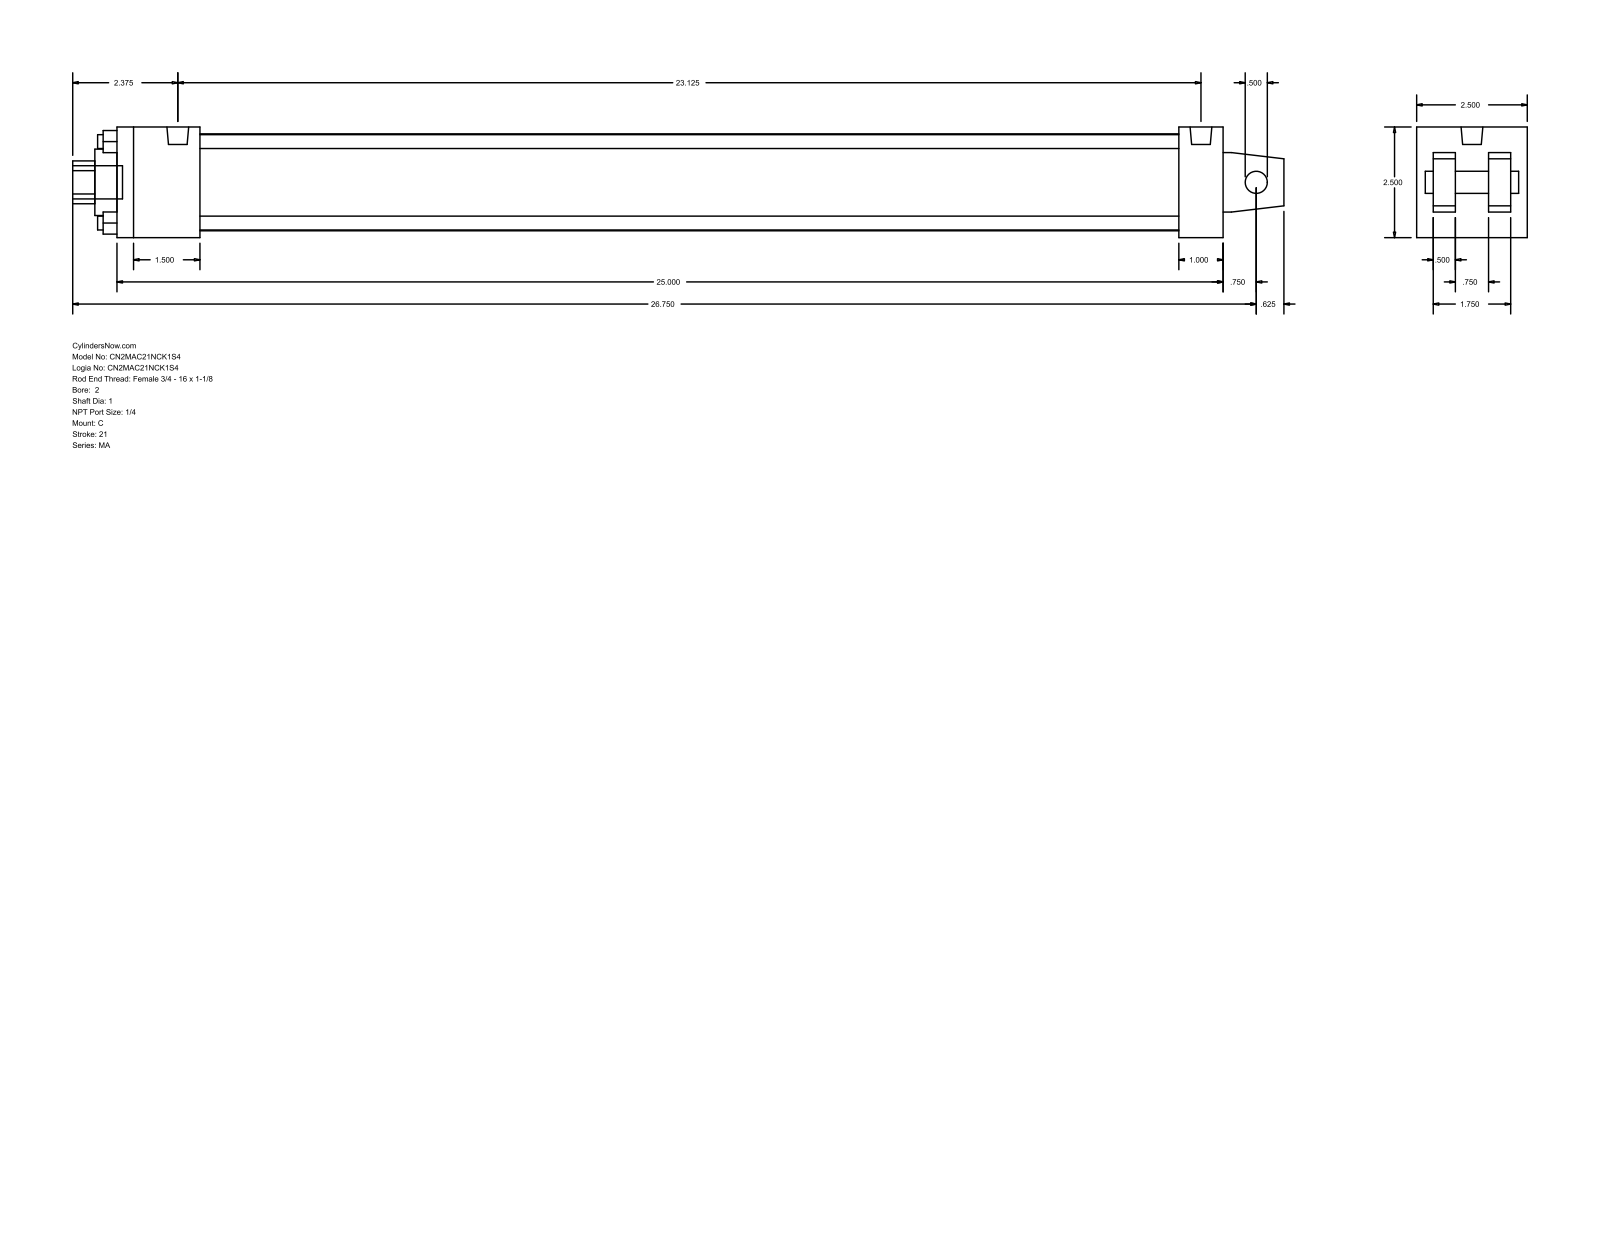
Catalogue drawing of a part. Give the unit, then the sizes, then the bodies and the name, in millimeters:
Units: millimetres
Overall size (bounding box): 695.33 × 63.5 × 63.5
Round holes (diameter × count): ⌀7.94 ×4, ⌀12.7 ×1, ⌀25.4 ×1, ⌀38.1 ×1, ⌀55.63 ×1
Round bosses / shafts (diameter × count): ⌀7.94 ×4, ⌀12.49 ×2, ⌀19.05 ×1
Partial cylindrical surfaces — rounded edges, fillets, slot ends (radius × count): R12.29 ×1
Main face-to-face distances: 63.5, 12.7, 635, 22.22, 41.28, 9.52, 53.98, 31.76, 47.63, 25.4
Hole centre spacings: 33.05, 46.74, 66.1
Bodies: 0 solids, 103 faces (76 planar, 27 cylindrical, 0 other)
Part name (STEP PRODUCT): MA_C__0200_1
STEP written by: GSSL Pune (CONFIG_CONTROL_DESIGN)
